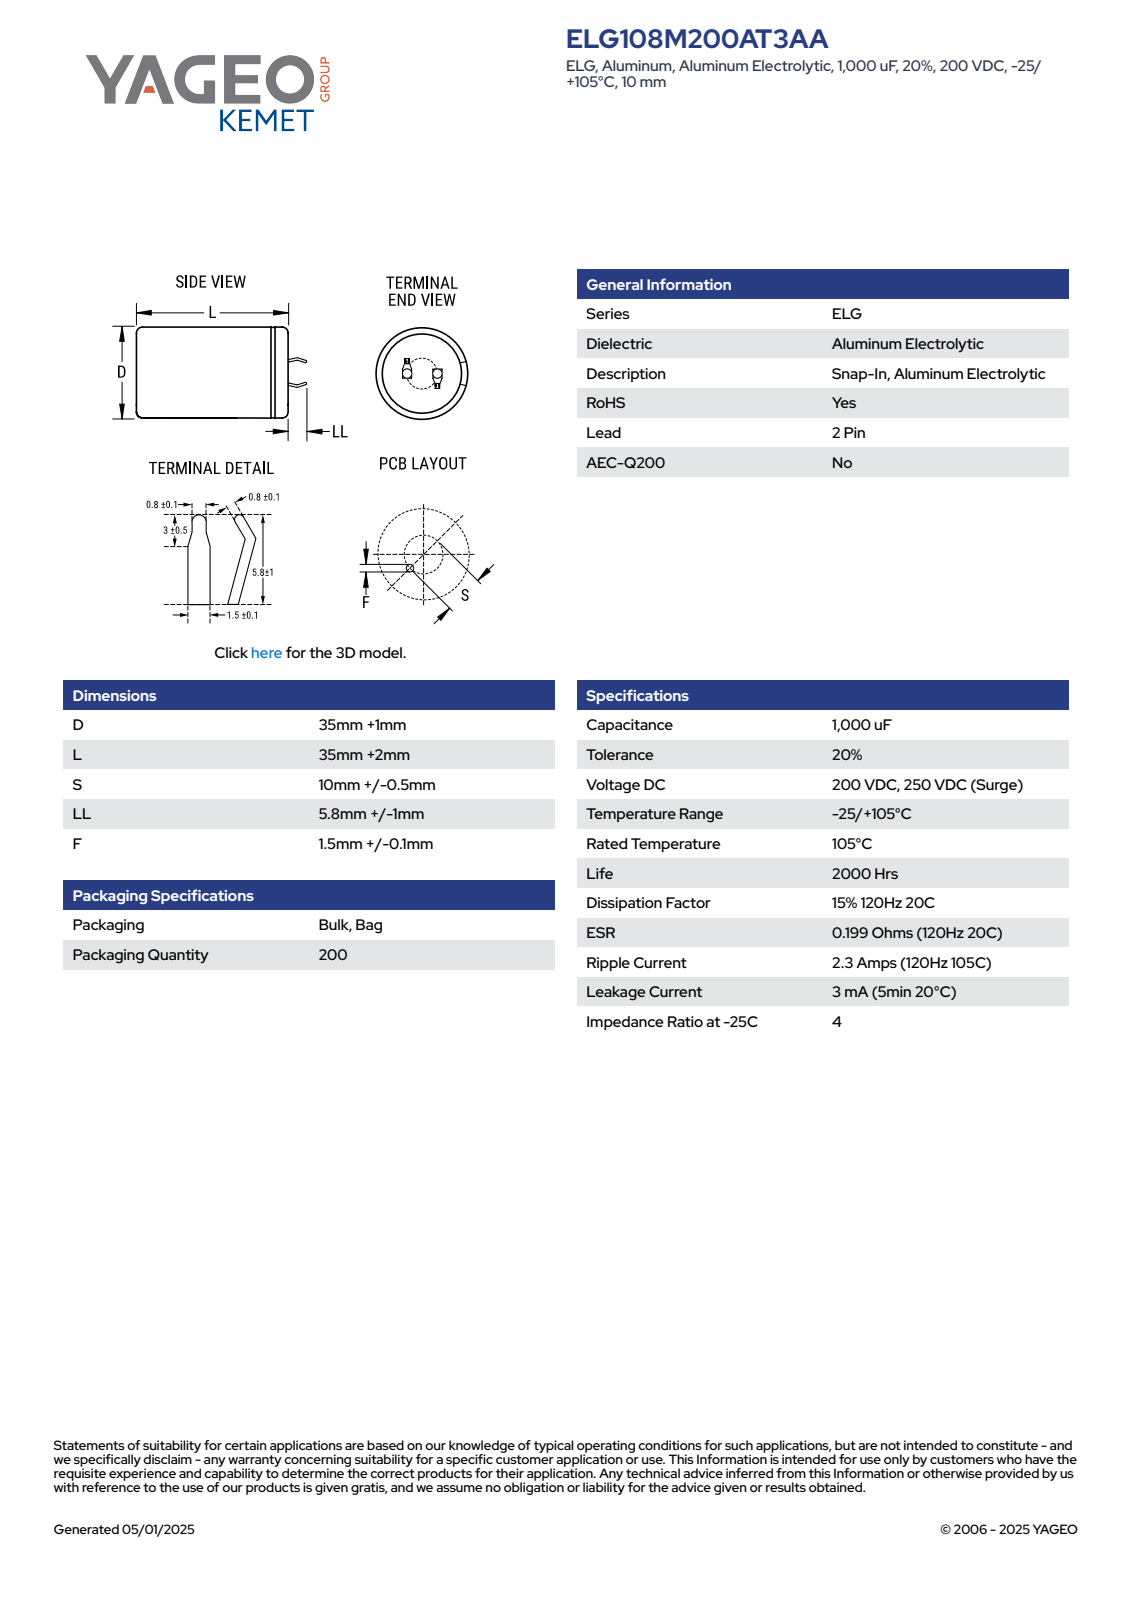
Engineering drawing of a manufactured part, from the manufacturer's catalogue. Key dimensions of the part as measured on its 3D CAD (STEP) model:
Part name (STEP PRODUCT): CARS_K2P_35X35_D36L37S10LL6.8F1.6
STEP written by: SolidWorks 2014 (AUTOMOTIVE_DESIGN)
Units: millimetres
Bodies: 1 solid, 100 faces (52 planar, 9 cylindrical, 39 other)
Overall size (bounding box): 43.79 × 36 × 36
Volume: 37 133 mm³ · Surface area: 6 215 mm²
Round holes (diameter × count): ⌀31.85 ×1
Round bosses / shafts (diameter × count): ⌀36 ×1
Partial cylindrical surfaces — rounded edges, fillets, slot ends (radius × count): R17.99 ×1
Main face-to-face distances: 36.99, 37.49, 0.5, 0.6, 7.08, 0.75, 1.35, 7.68, 6.48, 0.59
